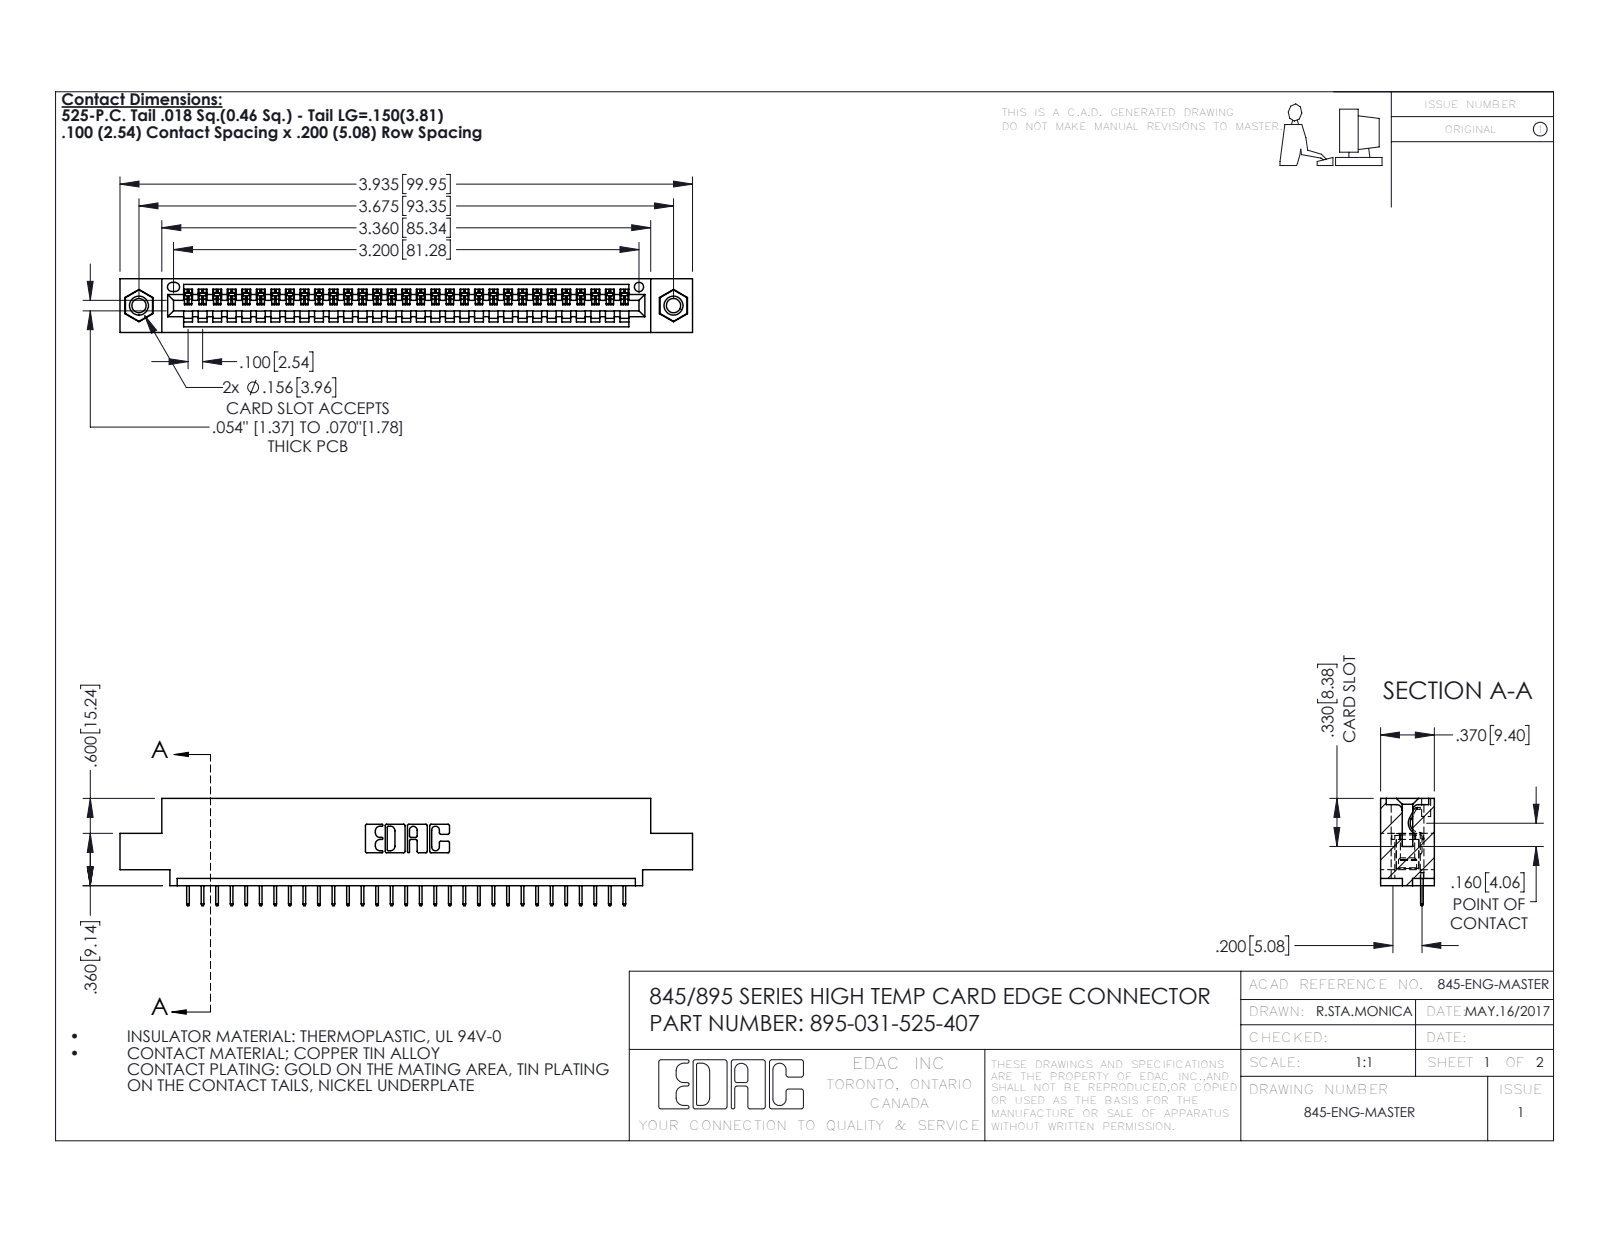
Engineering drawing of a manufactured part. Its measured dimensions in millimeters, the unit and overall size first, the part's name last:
Units: millimetres
Overall size (bounding box): 99.9 × 18.7 × 9.4
Round holes (diameter × count): ⌀2.5 ×2, ⌀3.2 ×2, ⌀4 ×2, ⌀1.6 ×1
Round bosses / shafts (diameter × count): ⌀3.9 ×2
Partial cylindrical surfaces — rounded edges, fillets, slot ends (radius × count): R0.2 ×62, R0.3 ×22, R0.2 ×6, R0.8 ×6, R0.7 ×3, R0.8 ×2, R1 ×2, R0.4 ×1
Main face-to-face distances: 1.8, 7.6, 9.4, 5.1, 2.5, 6.9, 0.6, 5.7, 1.8, 3.8
Hole centre spacings: 6.9, 87.4, 93.3
Volume: 9 190 mm³ · Surface area: 11 750 mm²
Bodies: 34 solids, 2112 faces (1542 planar, 554 cylindrical, 16 other)
Part name (STEP PRODUCT): 345-292-001_345-293-125; 345-250-001_345-250-005-103; 845 Part_0.110 Offset - 0.156 Dia-TI; 895-031-525-407
STEP written by: SolidWorks 2020 (CONFIG_CONTROL_DESIGN)
